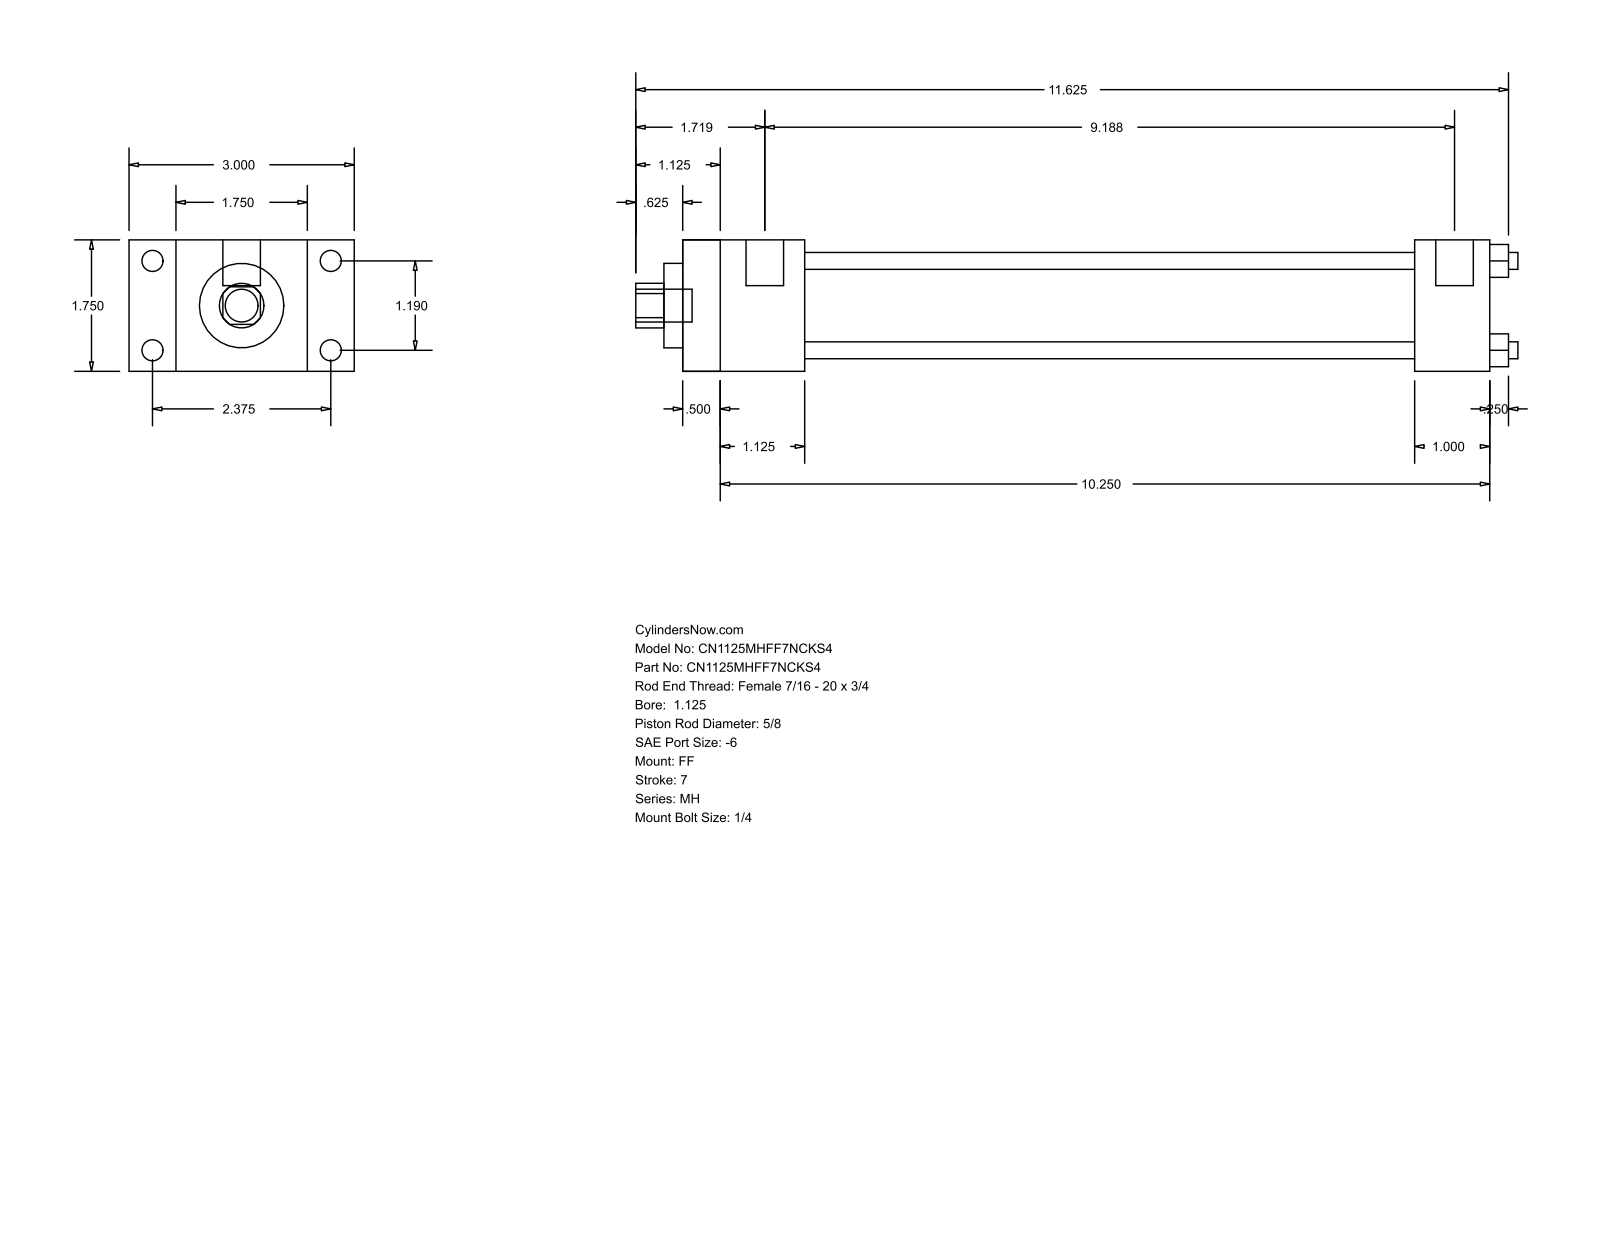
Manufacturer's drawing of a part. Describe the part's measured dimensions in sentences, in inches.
The part is named "MH_FF__0112_0.625". Its 3-D file was written by "GSSL Pune (CONFIG_CONTROL_DESIGN)". It is 0 solids with 92 faces: 64 planar, 28 cylindrical and 0 other. Overall it measures 11.75 by 3 by 1.75 inches. Round holes: 4 of diameter 0.225, 1 of diameter 0.625, 1 of diameter 1.125, 1 of diameter 1.375. Round bosses or shafts: 4 of diameter 0.281, 4 of diameter 0.219, 2 of diameter 0.5, 1 of diameter 0.437. Partial cylindrical surfaces (rounded edges, fillets, slot ends): 1 of radius 0.297. The main face-to-face distances are 1.75, 10.75, 0.625, 0.5, 10.25, 2.375, 1.125, 1.625, 9.75, 9.25. The hole center spacings are 0.841, 1.19, 1.683.
